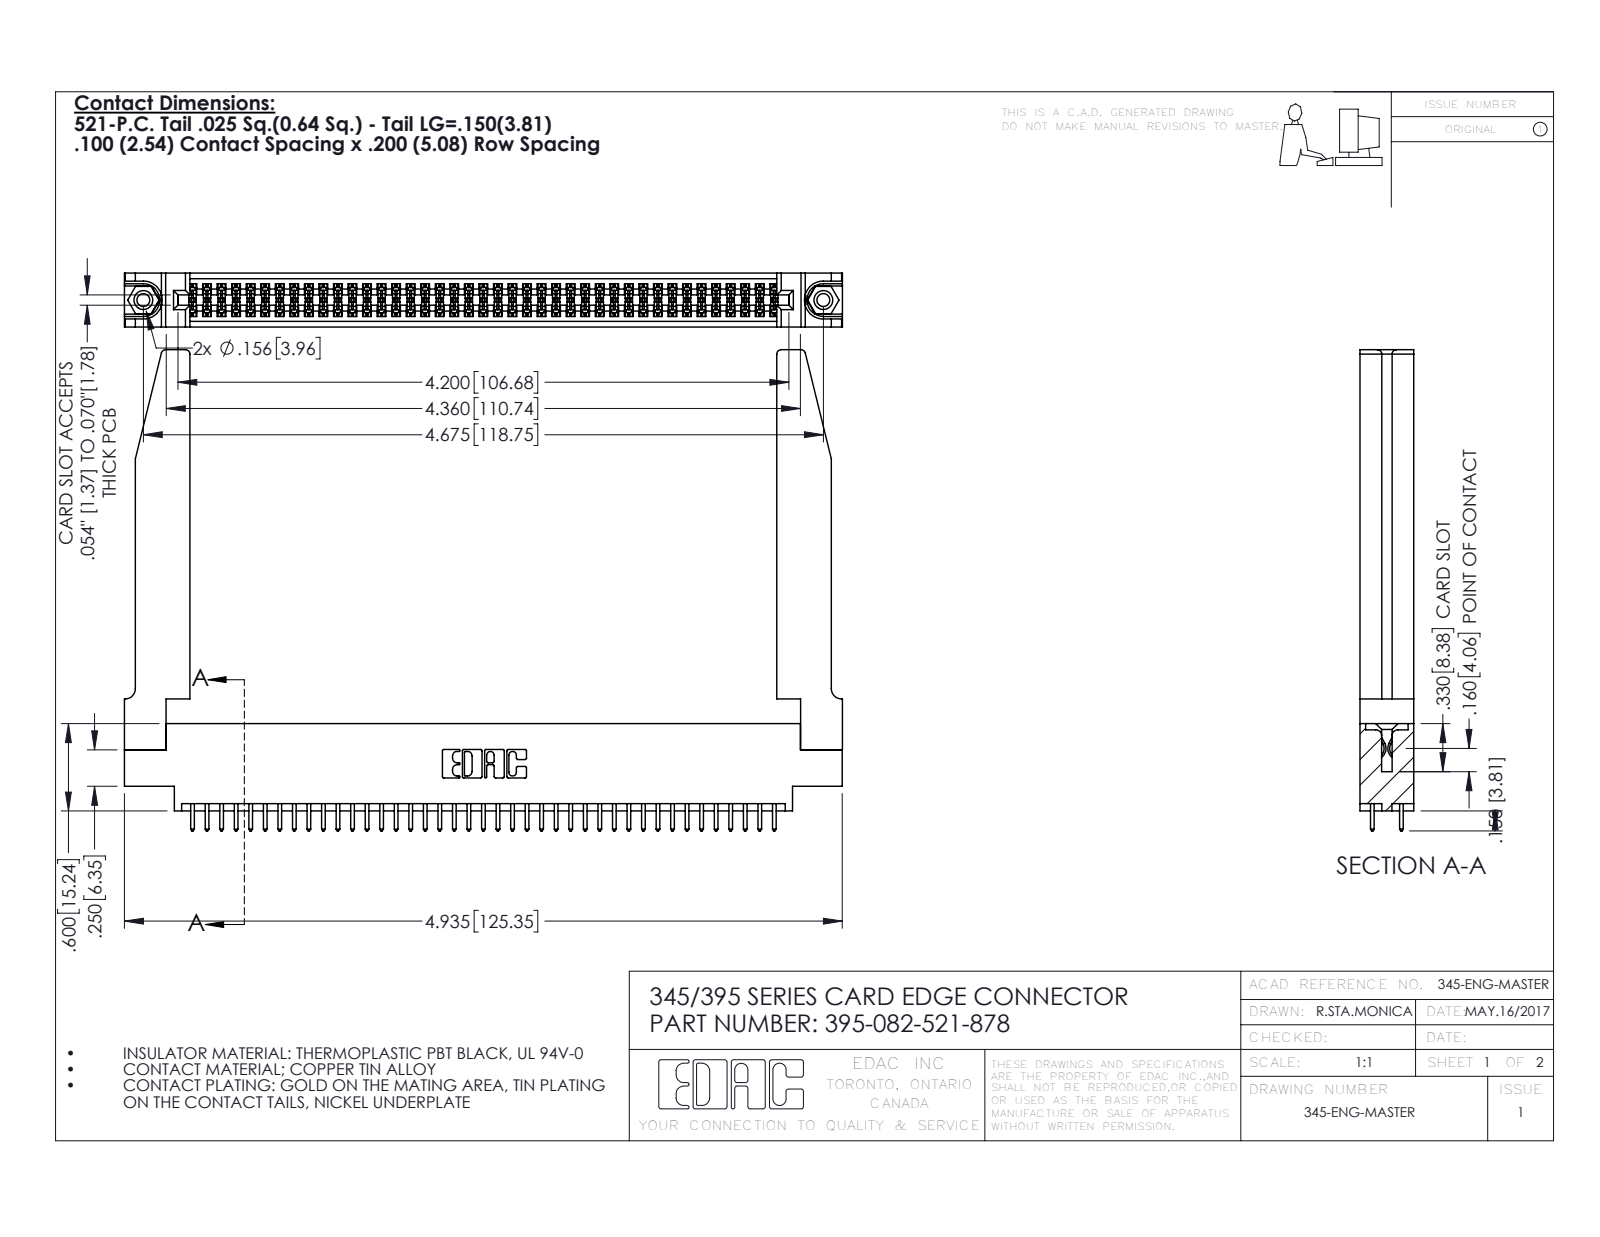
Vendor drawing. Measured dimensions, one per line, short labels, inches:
name: 345-292-001_345-293-121; 345 Part_0.170 Offset - 0.156 Dia-TH; 345-250-001_345-250-001-102; 345-220-078_345-220-078 (+1 more)
written by: SolidWorks 2016 (CONFIG_CONTROL_DESIGN)
unit: in
bodies: 87 solids, 4464 faces (2932 planar, 1480 cylindrical, 52 other)
size: 4.936 × 3.307 × 0.37
volume: 1.208 in³; area: 38 in²
holes: 2× ⌀0.089, 2× ⌀0.125, 2× ⌀0.156, 1× ⌀0.064
bosses: 2× ⌀0.155
rounds: 123× R0.006, 82× R0.01, 22× R0.01, 8× R0.03, 6× R0.007, 6× R0.031, 3× R0.026, 2× R0.014
face distances: 0.37, 0.072, 0.298, 0.2, 0.098, 0.272, 0.025, 0.225, 0.175, 0.148
hole spacings: 0.27, 4.439, 4.675
